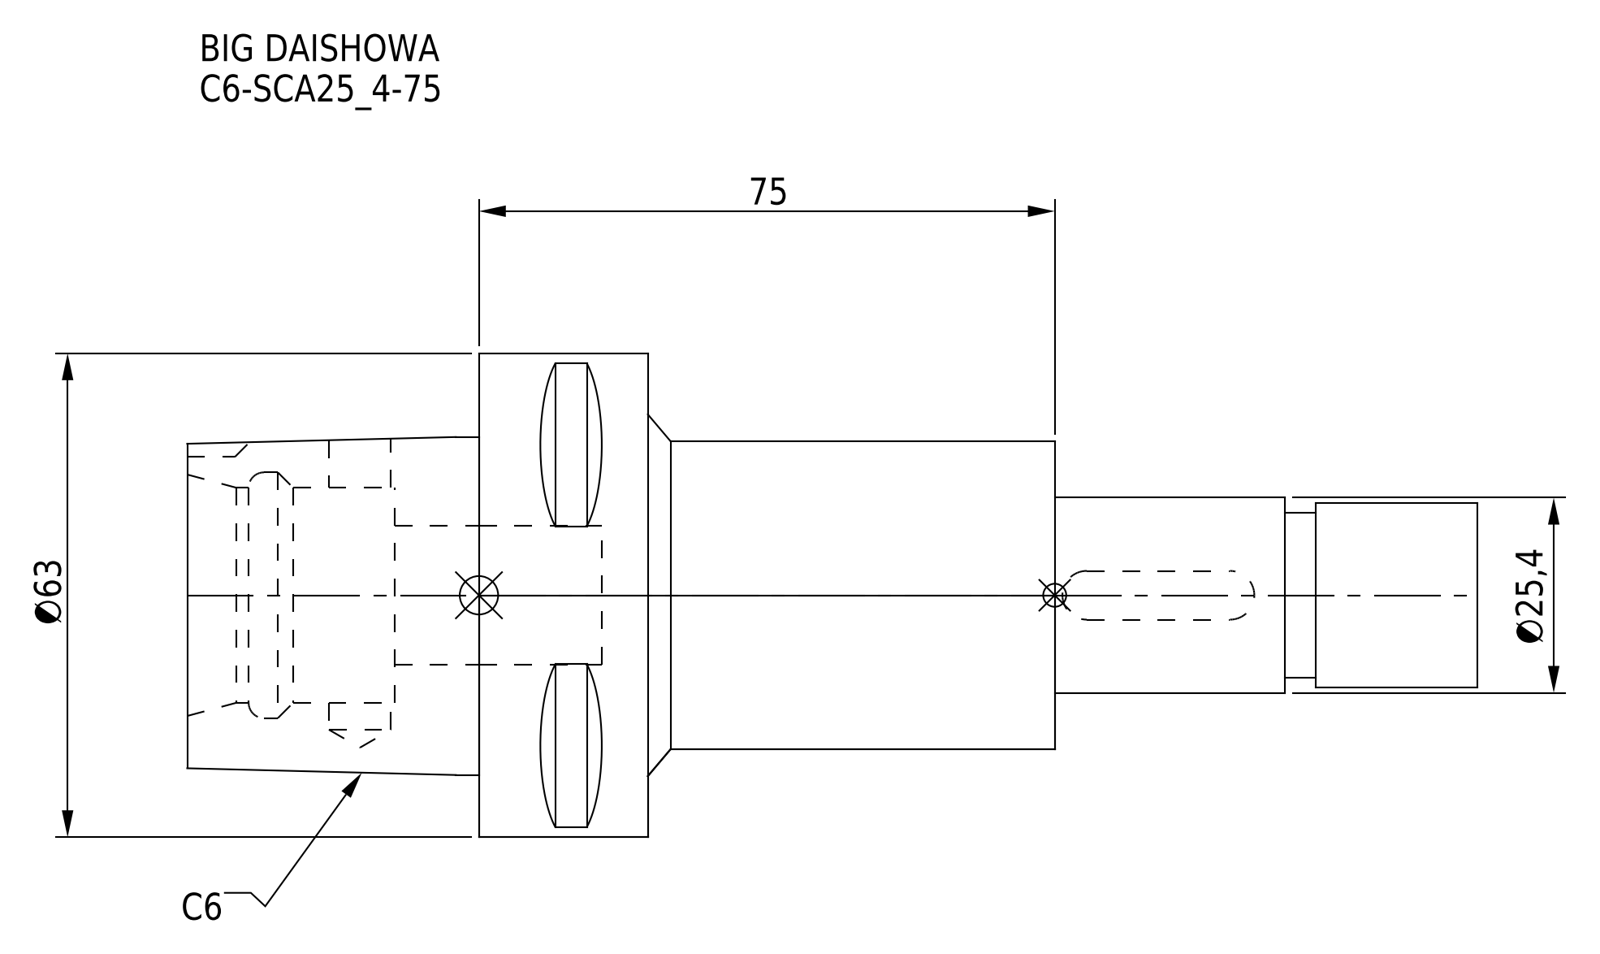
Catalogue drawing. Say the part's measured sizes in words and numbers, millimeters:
The part is named "C6-SCA25_4-75". Its 3-D file was written by "CREO PARAMETRIC BY PTC INC, 2016380 (AUTOMOTIVE_DESIGN)". It is 1 solid with 71 faces: 34 planar, 25 cylindrical and 12 other. Overall it measures 168 by 63 by 63 millimeters. Its volume is 190 412 cubic millimeters and its surface area 31 158 square millimeters. Round holes: 1 of diameter 8.1, 1 of diameter 18, 1 of diameter 28, 1 of diameter 32. Round bosses or shafts: 1 of diameter 63, 1 of diameter 40, 1 of diameter 25.4, 1 of diameter 24, 1 of diameter 21.5. Partial cylindrical surfaces (rounded edges, fillets, slot ends): 2 of radius 3.17, 1 of radius 5. The main face-to-face distances are 22, 53, 75, 27, 113, 60, 38, 55, 108, 130.
